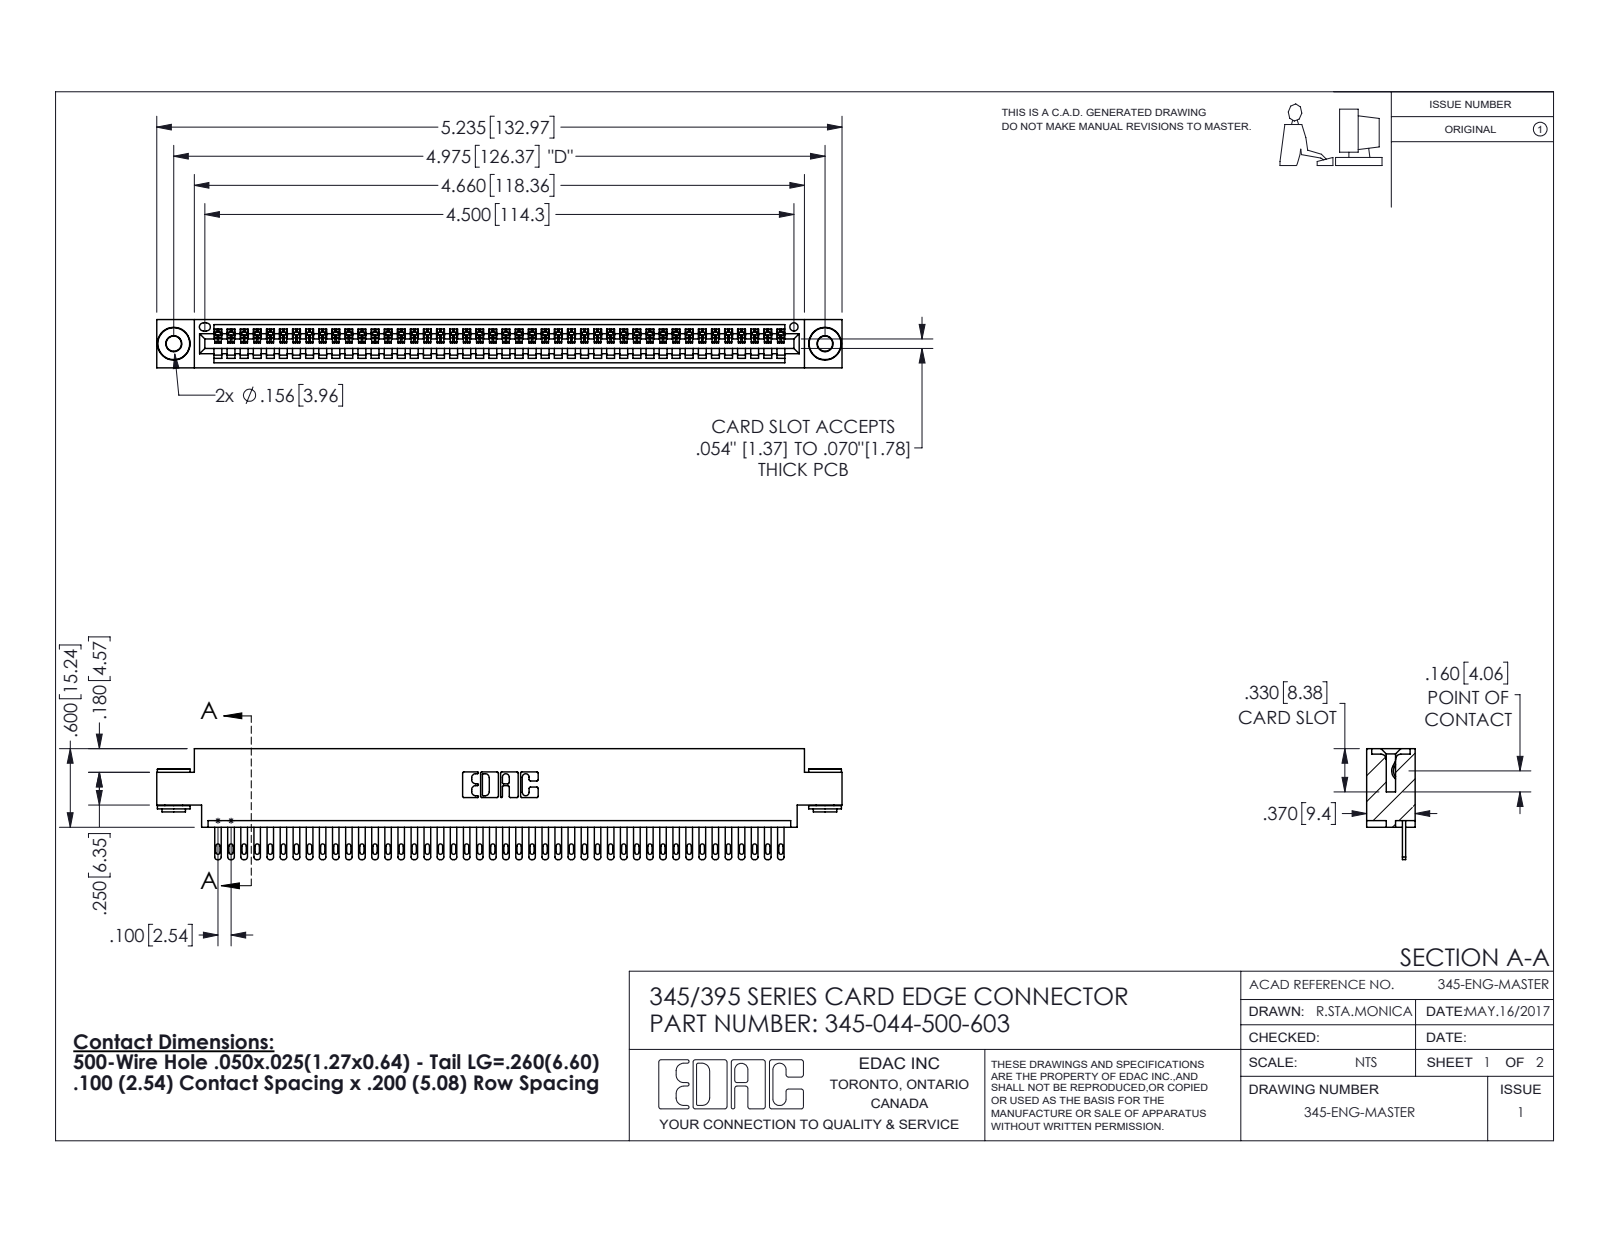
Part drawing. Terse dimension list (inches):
name: 345-044-500-603; 345-250-002_345-250-002-102; 345-292-001_345-293-100; 345 Part_0.170 Offset - 0.156 Dia-TH
written by: SolidWorks 2016 (CONFIG_CONTROL_DESIGN)
unit: in
bodies: 47 solids, 2544 faces (1590 planar, 946 cylindrical, 8 other)
size: 5.235 × 0.847 × 0.37
volume: 0.768 in³; area: 26.63 in²
holes: 2× ⌀0.116, 2× ⌀0.156, 1× ⌀0.064
bosses: 2× ⌀0.25, 2× ⌀0.18, 2× ⌀0.136
rounds: 88× R0.006, 88× R0.016, 88× R0.02, 22× R0.01, 6× R0.007, 6× R0.031, 3× R0.026, 2× R0.031
face distances: 0.072, 0.298, 0.37, 0.098, 0.272, 0.025, 0.2, 0.225, 0.175, 0.149
hole spacings: 0.27, 4.739, 4.975
